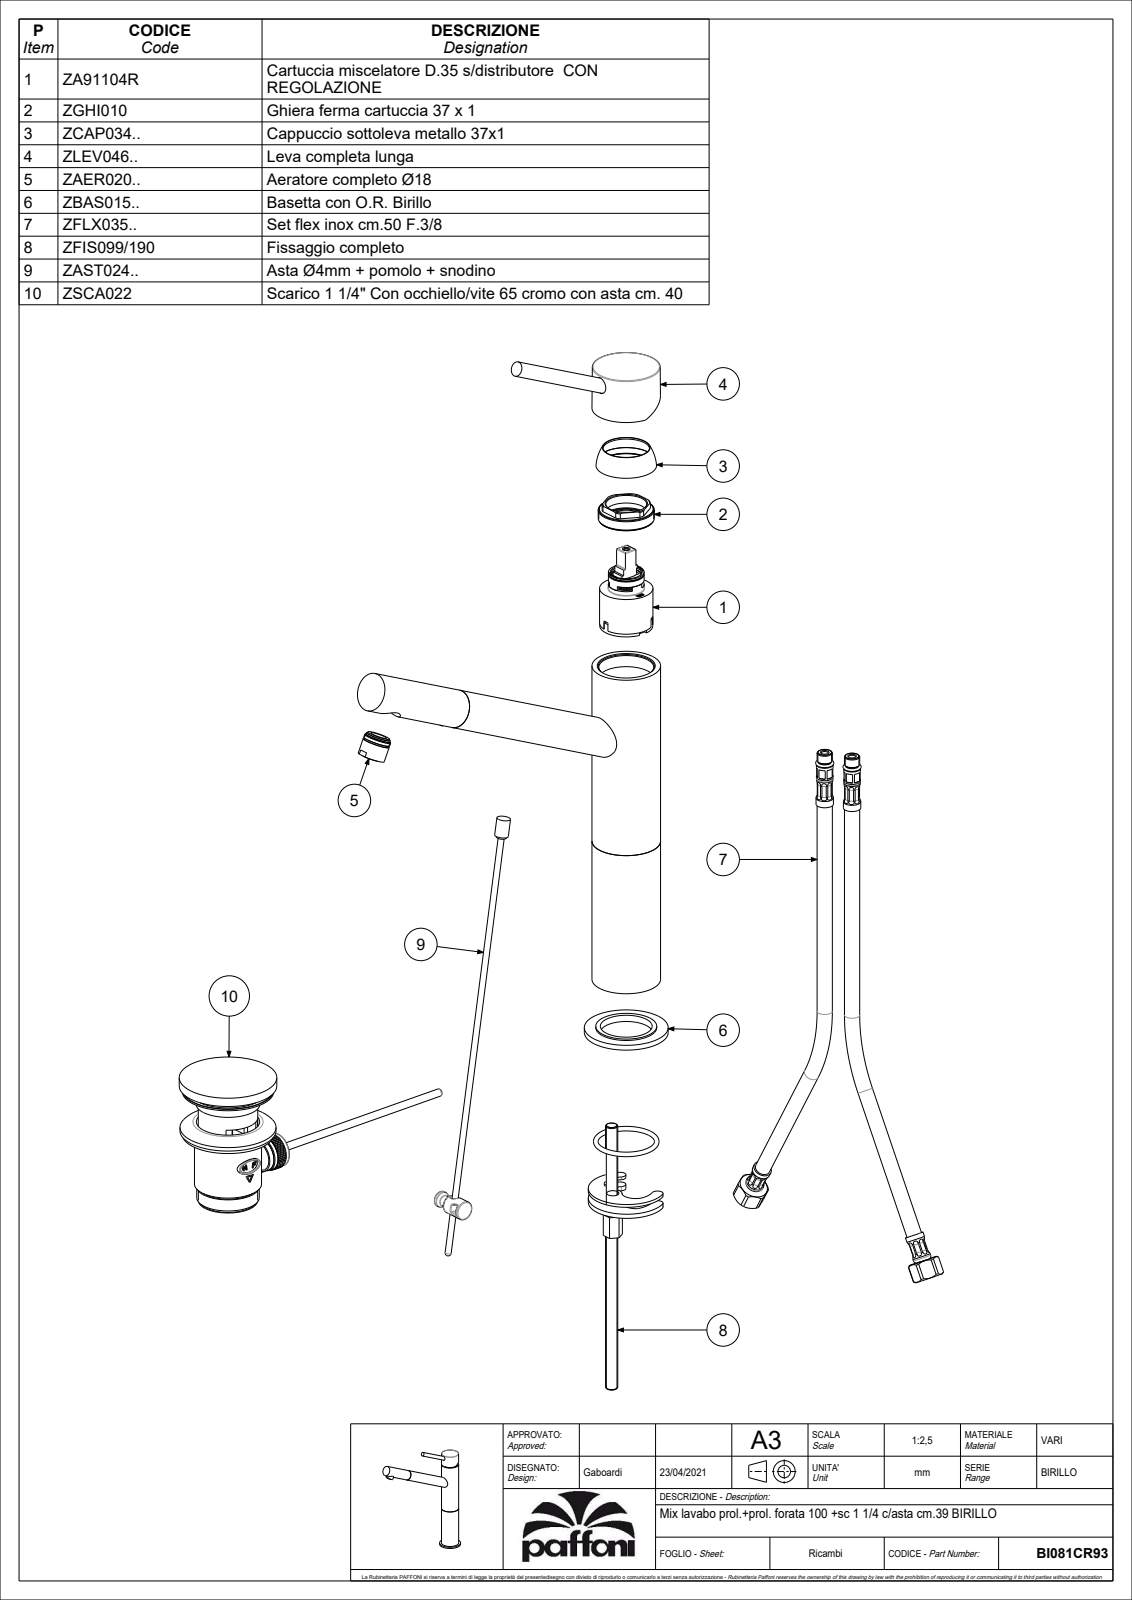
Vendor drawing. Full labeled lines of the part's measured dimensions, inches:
Part name (STEP PRODUCT): BI081CR93
STEP written by: CREO PARAMETRIC BY PTC INC, 2020044 (CONFIG_CONTROL_DESIGN)
Units: inches
Bodies: 3 solids, 1117 faces (613 planar, 270 cylindrical, 234 other)
Overall size (bounding box): 11.529 × 10.332 × 2.165
Volume: 21.53 in³ · Surface area: 171.7 in²
Round holes (diameter × count): ⌀0.433 ×3, ⌀0.157 ×2, ⌀0.177 ×2, ⌀0.197 ×2, ⌀0.256 ×2, ⌀0.354 ×2, ⌀0.13 ×1, ⌀0.217 ×1, ⌀0.268 ×1, ⌀0.394 ×1, ⌀0.61 ×1, ⌀0.724 ×1
Round bosses / shafts (diameter × count): ⌀2.165 ×1, ⌀1.772 ×1, ⌀1.591 ×1, ⌀1.575 ×1, ⌀1.457 ×1, ⌀1.378 ×1, ⌀1.37 ×1, ⌀1.268 ×1
Partial cylindrical surfaces — rounded edges, fillets, slot ends (radius × count): R0.02 ×51, R0.006 ×11, R0.012 ×4, R0.039 ×2, R0.041 ×1, R0.098 ×1, R0.118 ×1, R0.197 ×1
Main face-to-face distances: 4.843, 0.039, 0.138, 0.217, 8.858, 8.043, 7.906, 4.98, 3.063, 0.079
Hole centre spacings: 0.139, 0.317, 0.344, 0.432, 0.552, 0.626, 0.492, 0.591
